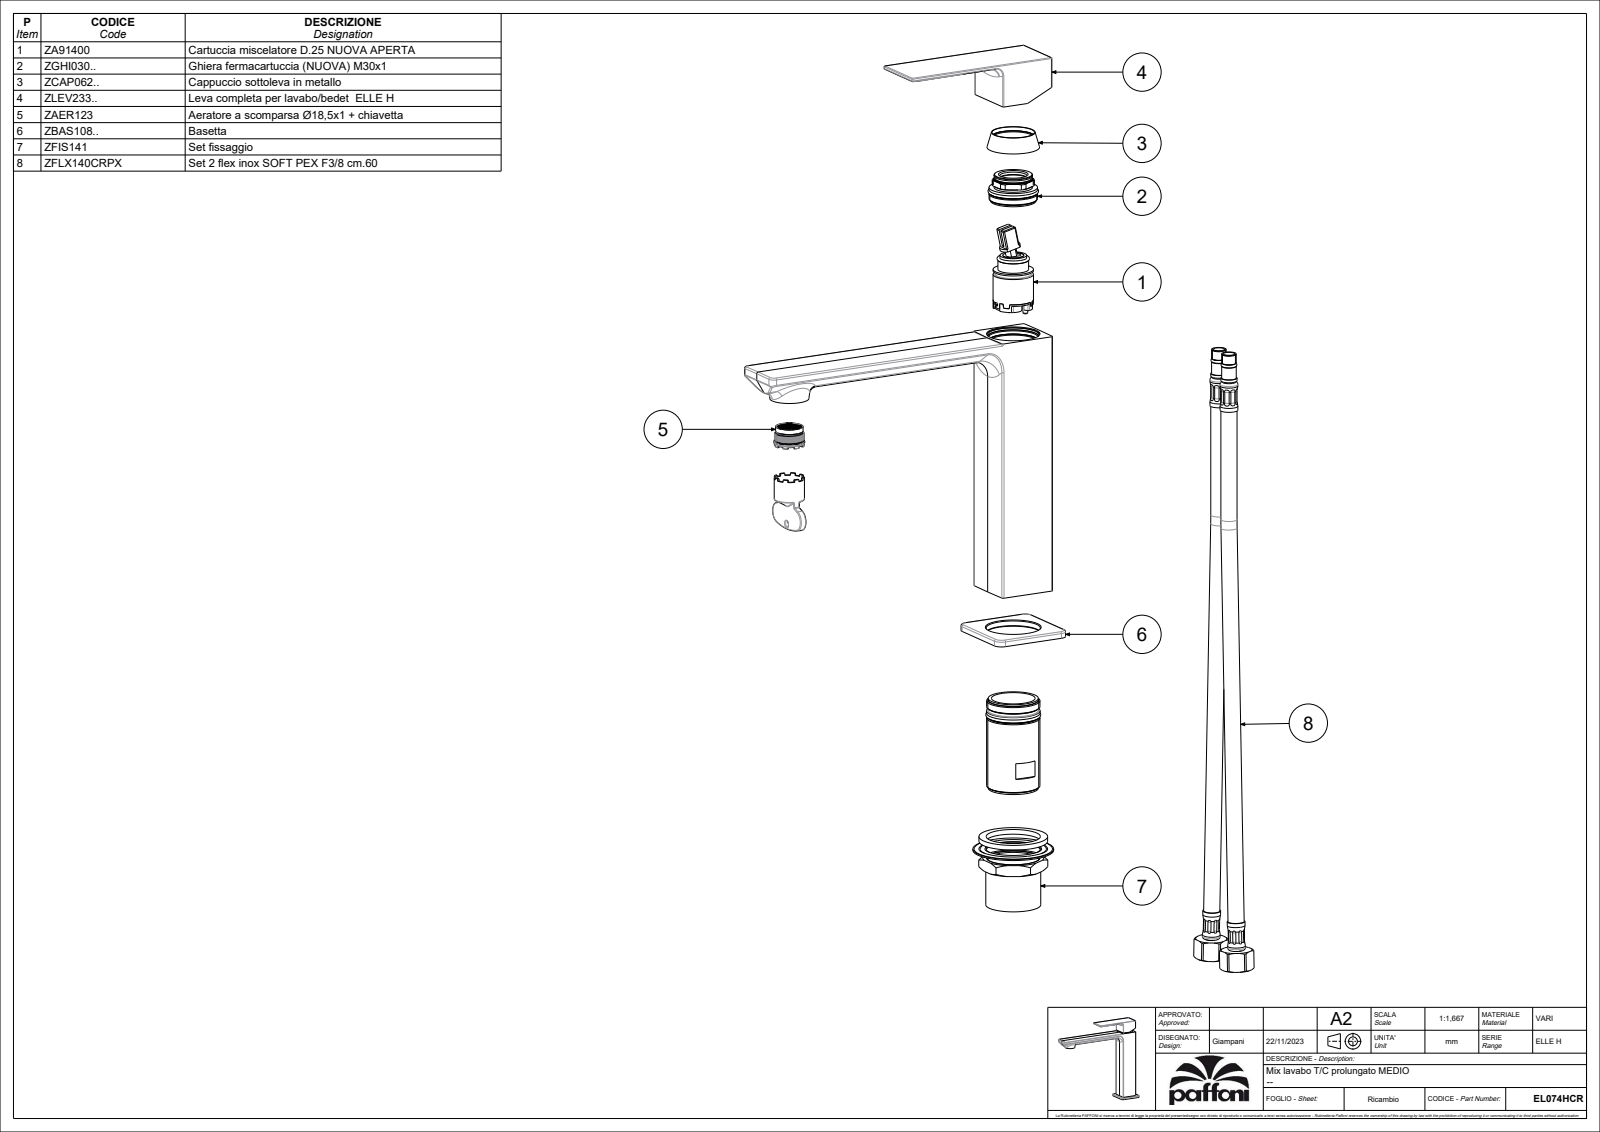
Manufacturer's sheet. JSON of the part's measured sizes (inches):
{"part_name": "EL074HCR", "step_written_by": "CREO PARAMETRIC BY PTC INC, 2022124 (CONFIG_CONTROL_DESIGN)", "units": "inches", "bodies": {"solids": 2, "faces": 4647, "planar": 3505, "cylindrical": 714, "other": 428}, "overall_size": [8.199, 7.69, 1.969], "volume_in3": 10.66, "surface_area_in2": 146.9, "round_holes": [[0.126, 2], [0.165, 2], [0.197, 2], [0.276, 2], [0.339, 2], [0.37, 2], [0.118, 1], [0.13, 1], [0.543, 1], [0.551, 1], [0.555, 1], [0.591, 1]], "round_bosses_or_shafts": [[0.031, 6], [0.118, 2], [1.535, 1], [1.079, 1], [0.984, 1], [0.89, 1], [0.799, 1], [0.732, 1]], "partial_cylinders_radius": [[0.005, 89], [0.085, 40], [0.02, 25], [0.039, 25], [0.066, 12], [0.03, 6], [0.008, 4], [0.012, 4]], "face_to_face_distances": [0.136, 1.146, 1.169, 0.116, 1.262, 1.378, 0.02, 7.67, 1.281, 1.398], "hole_center_spacings": [0.433, 0.06, 0.265, 0.303, 0.342, 0.352, 0.367, 0.419]}
